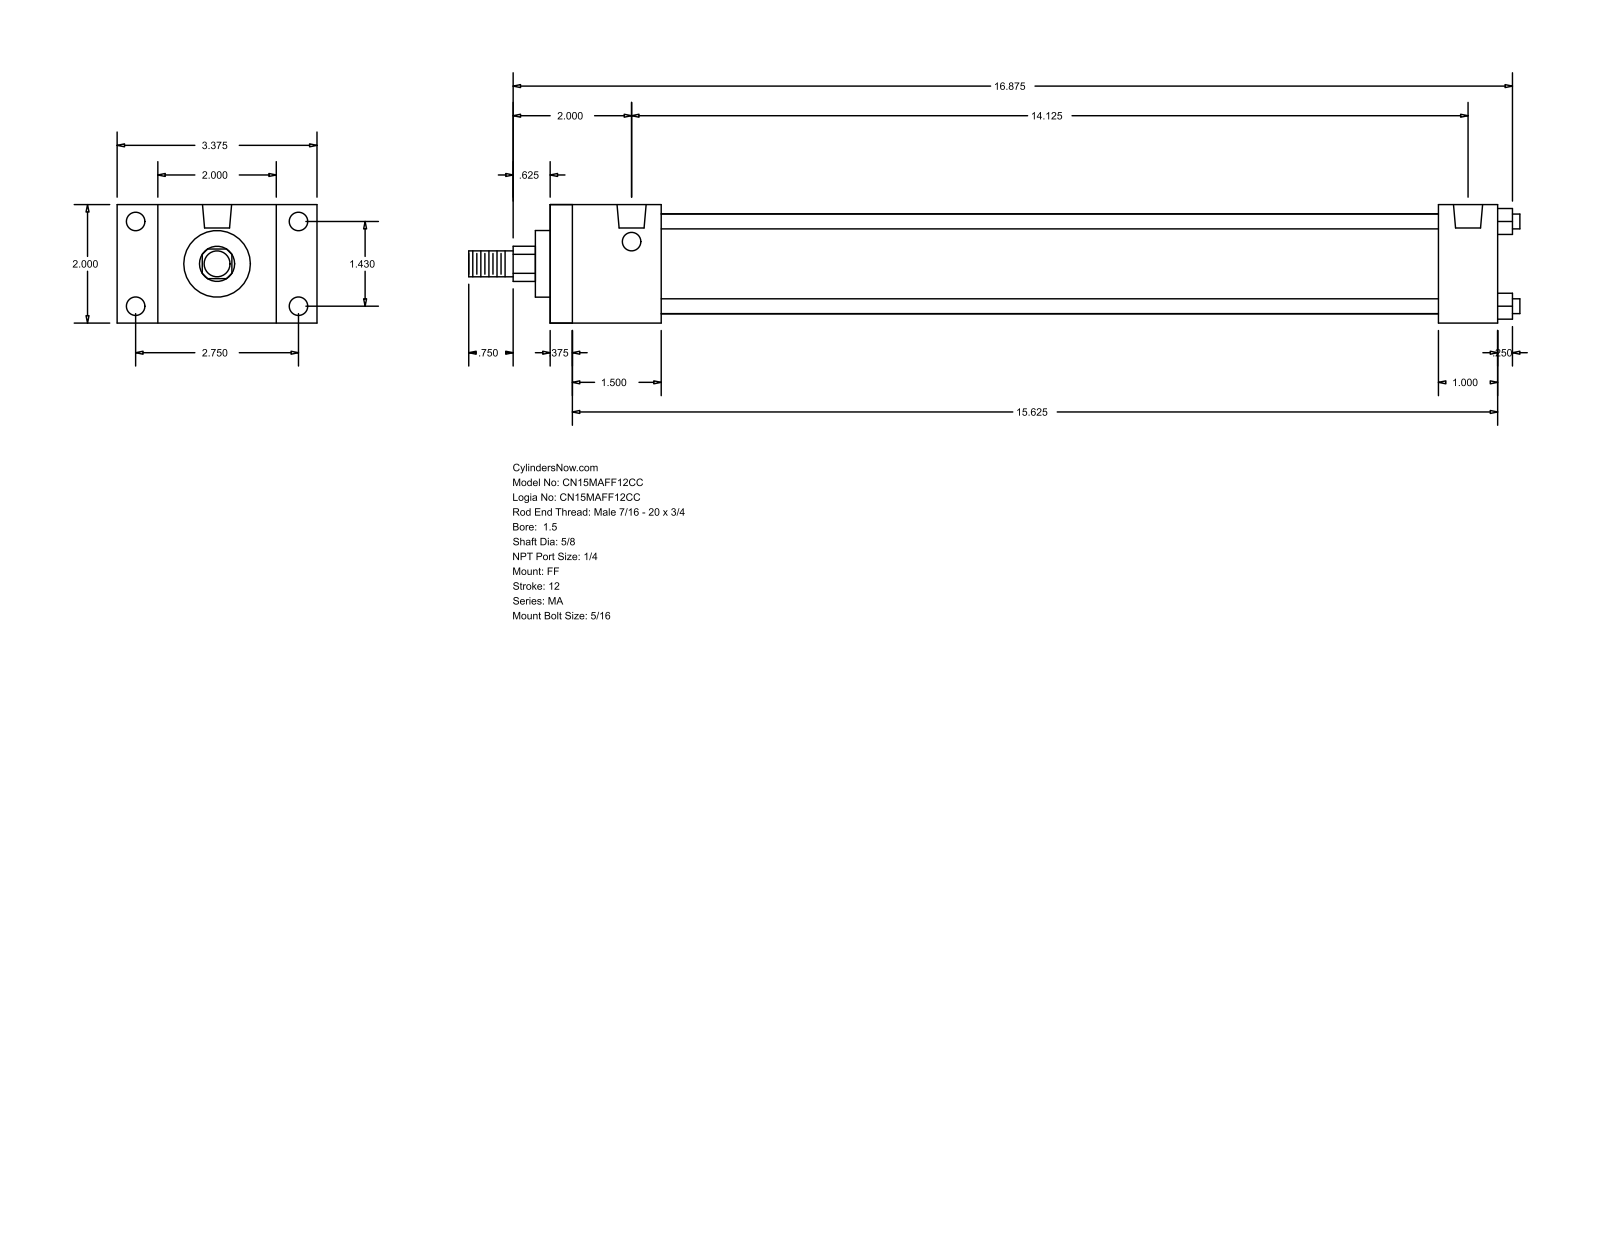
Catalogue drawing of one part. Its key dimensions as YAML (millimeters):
part_name: "MA_FF__0150_0.625"
step_written_by: "GSSL Pune (CONFIG_CONTROL_DESIGN)"
units: millimeters
bodies: {solids: 0, faces: 92, planar: 64, cylindrical: 28, other: 0}
overall_size: [450.85, 85.72, 50.8]
round_holes:
  - {diameter: 7.94, count: 8}
  - {diameter: 12.49, count: 2}
round_bosses_or_shafts:
  - {diameter: 6.35, count: 4}
  - {diameter: 42.93, count: 1}
  - {diameter: 28.57, count: 1}
  - {diameter: 15.88, count: 1}
  - {diameter: 11.11, count: 1}
partial_cylinders:
  - {radius: 7.54, count: 1}
face_to_face_distances: [50.8, 406.39, 9.52, 396.87, 47.62, 381, 38.1, 371.48, 333.38, 358.77]
hole_center_spacings: [36.32, 69.84, 78.72, 358.77]
